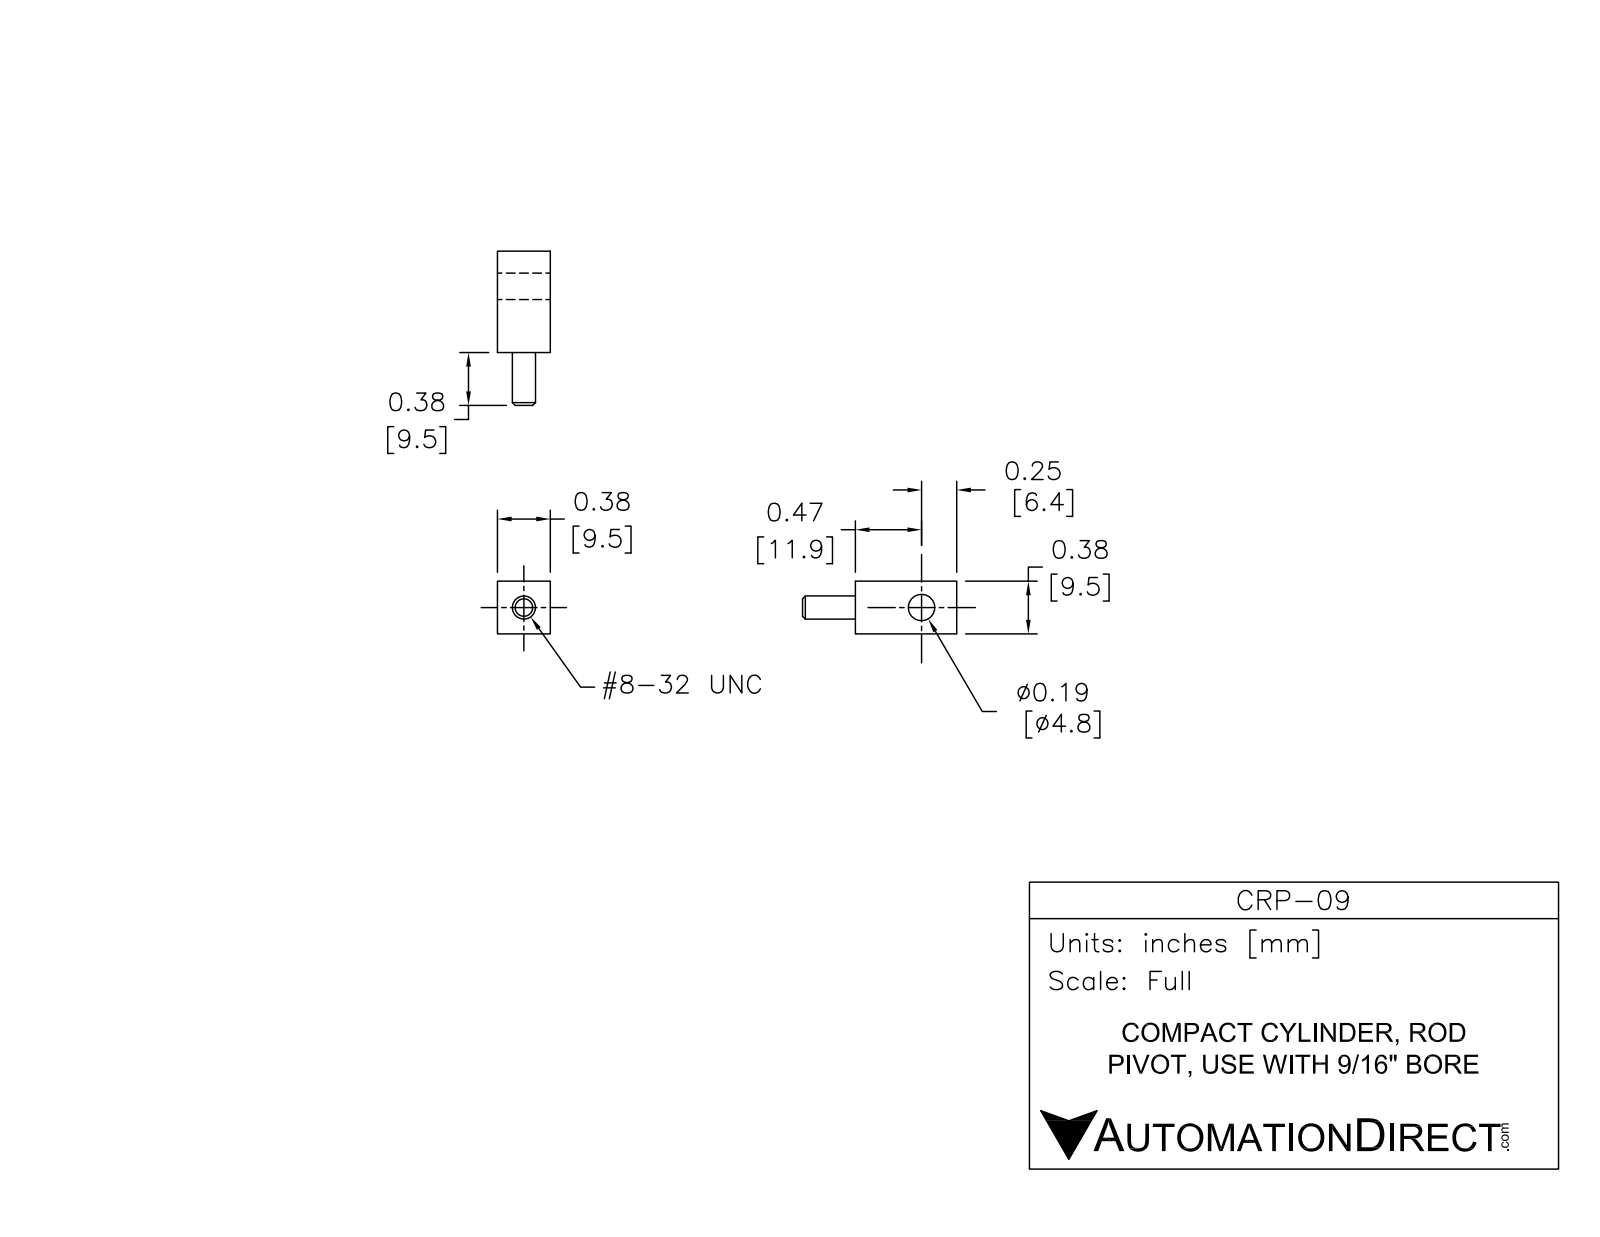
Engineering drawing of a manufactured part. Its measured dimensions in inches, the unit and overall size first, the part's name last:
Units: inches
Overall size (bounding box): 1.1 × 0.397 × 0.38
Round holes (diameter × count): ⌀0.13 ×1, ⌀0.19 ×1, ⌀0.252 ×1
Round bosses / shafts (diameter × count): ⌀0.164 ×1
Main face-to-face distances: 0.38, 0.72, 0.12, 0.84, 0.344, 0.018, 0.362, 0.26, 0.38, 1.1
Volume: 0.112 in³ · Surface area: 2.702 in²
Bodies: 3 solids, 45 faces (17 planar, 10 cylindrical, 18 other)
Part name (STEP PRODUCT): CRP-09_nut; CRP-09; CRP-09_bracket; CRP-09_bushing
STEP written by: SolidWorks 2014 (AUTOMOTIVE_DESIGN)
